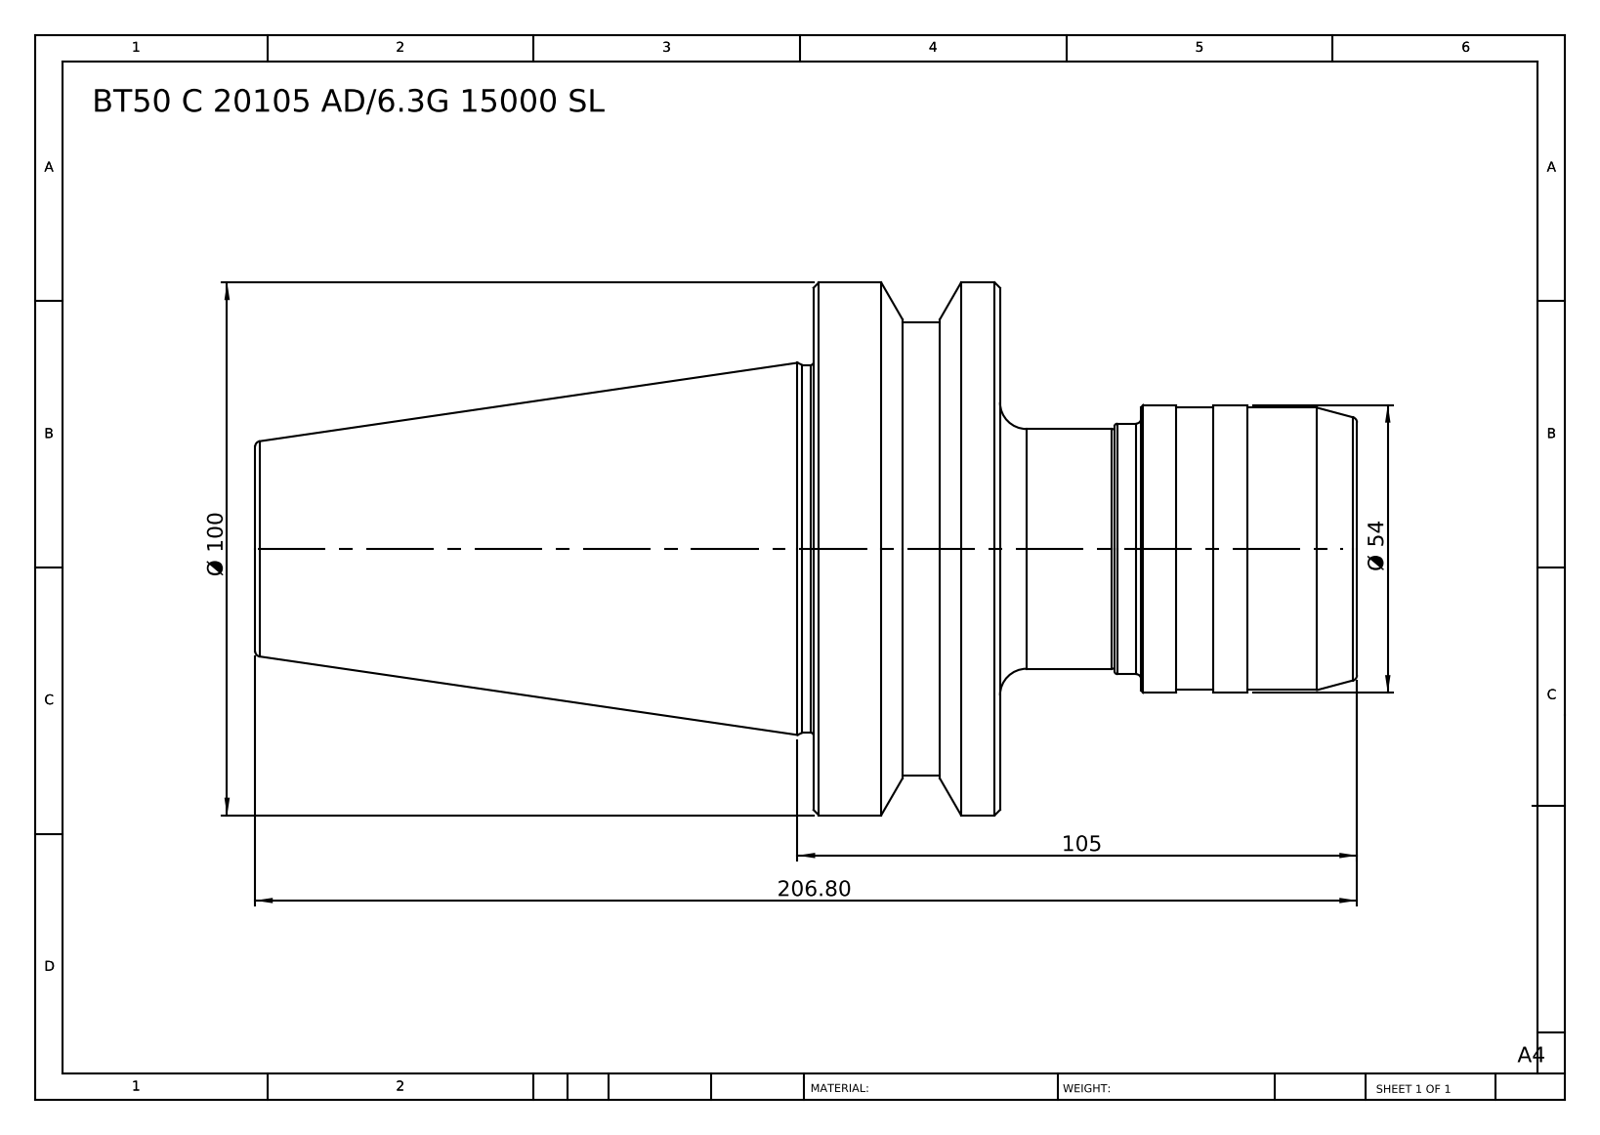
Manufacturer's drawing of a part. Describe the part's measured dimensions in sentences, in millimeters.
The part is named "BT50 C20 105 AD-6.3G 15000 SL". Its 3-D file was written by "SolidWorks 2014 (CONFIG_CONTROL_DESIGN)". It is 1 solid with 61 faces: 11 planar, 20 cylindrical and 30 other. Overall it measures 206.8 by 100 by 100 millimeters. Its volume is 642 914 cubic millimeters and its surface area 55 730 square millimeters. Round bosses or shafts: 1 of diameter 100, 1 of diameter 85, 1 of diameter 69, 1 of diameter 54, 1 of diameter 53, 1 of diameter 47, 1 of diameter 45. The main face-to-face distances are 35, 67, 102, 206.8, 139.8, 104.8, 40.5, 26.5, 61.5, 166.3.
